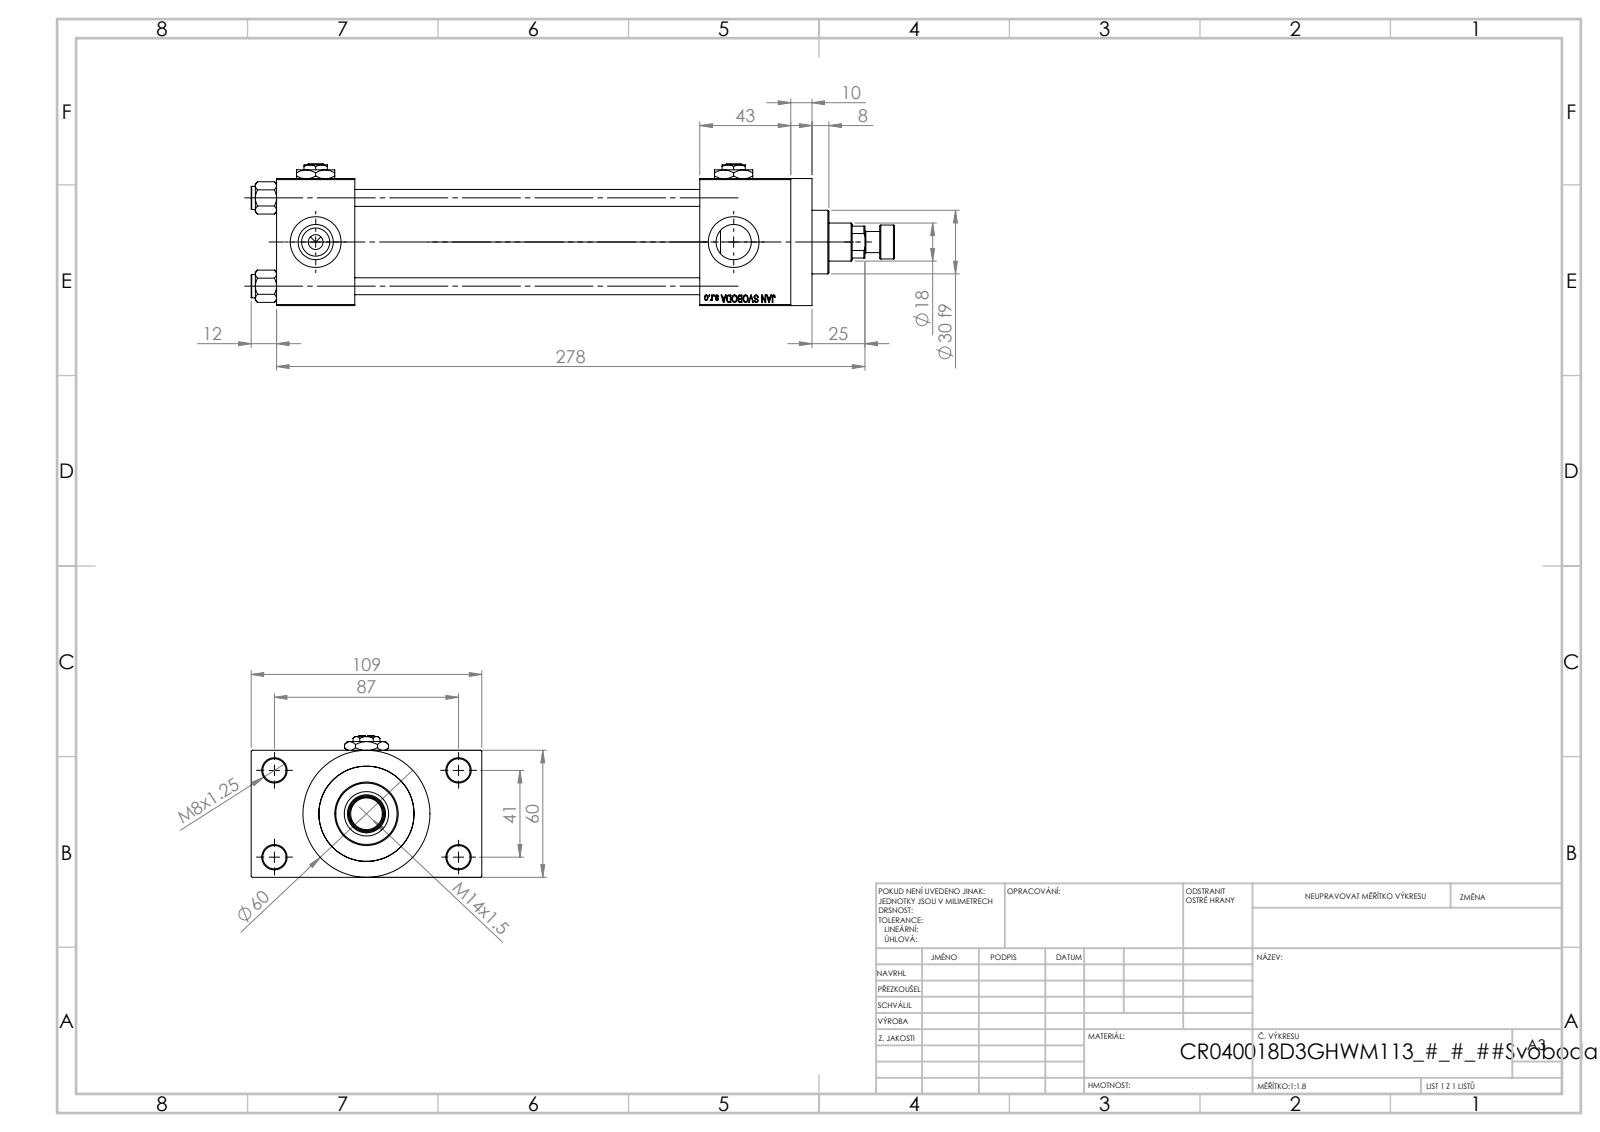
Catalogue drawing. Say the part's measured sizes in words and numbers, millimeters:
The part is named "V215CR_D_Body; Zatka_pro_OIL_PORT; NUT_M5_D; V215_VC_A (+3 more)". Its 3-D file was written by "SolidWorks 2019 (CONFIG_CONTROL_DESIGN)". It is 14 solids with 1218 faces: 549 planar, 103 cylindrical and 566 other. Overall it measures 304 by 109 by 67 millimeters. Its volume is 602 677 cubic millimeters and its surface area 171 030 square millimeters. Round holes: 4 of diameter 8, 4 of diameter 11, 4 of diameter 16.66, 4 of diameter 24, 3 of diameter 7, 1 of diameter 8.5, 1 of diameter 18, 1 of diameter 21, 1 of diameter 31, 1 of diameter 40, 1 of diameter 45. Round bosses or shafts: 4 of diameter 11, 1 of diameter 60, 1 of diameter 46, 1 of diameter 30, 1 of diameter 16, 1 of diameter 10. Partial cylindrical surfaces (rounded edges, fillets, slot ends): 1 of radius 8.5. The main face-to-face distances are 60, 24.5, 163, 84.5, 37, 200, 43, 243, 206, 10. The hole center spacings are 22.65, 29.49, 41.7, 47.15, 48.09, 64.35, 76.49, 41.
